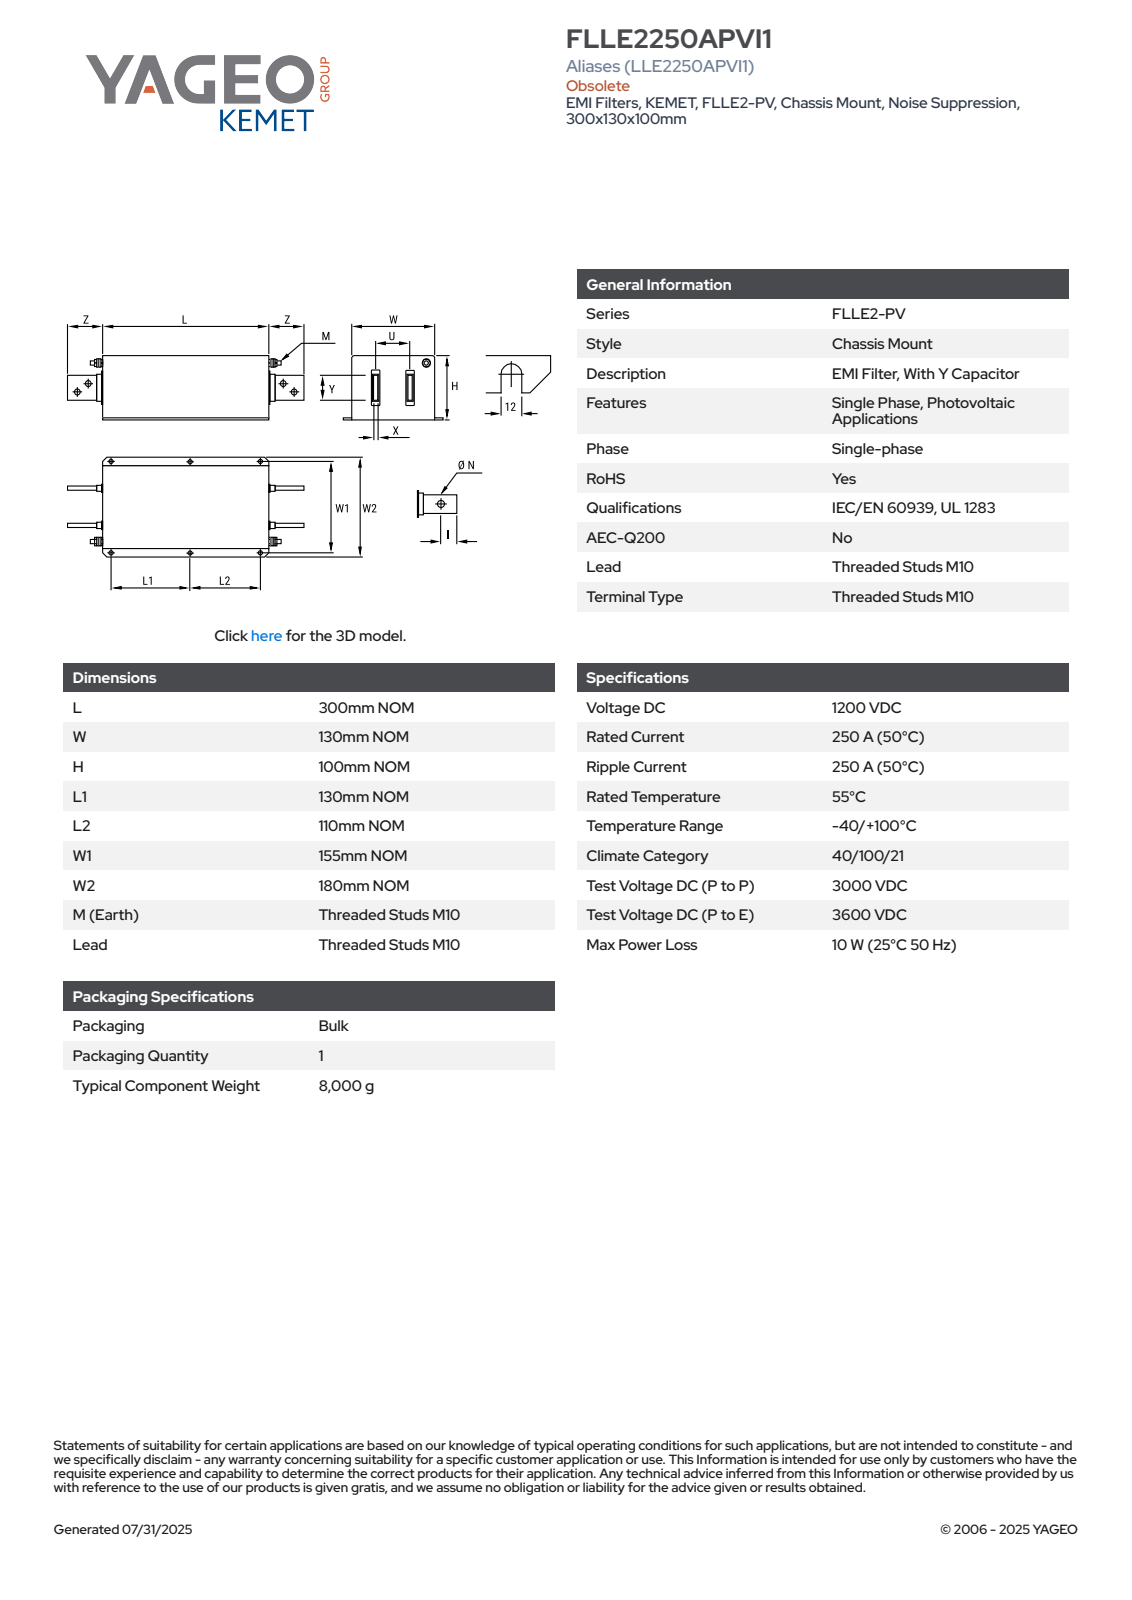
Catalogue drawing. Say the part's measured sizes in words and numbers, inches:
The part is named "HEX NUT M10x1.5_90592A024; HEX BOLT M10x35_91280A636; LOCK WASHER M10_91169A210; Busbar 5x20^FLLE2250APVI1_EXT (+8 more)". Its 3-D file was written by "SolidWorks 2021 (AUTOMOTIVE_DESIGN)". It is 56 solids with 1898 faces: 500 planar, 556 cylindrical and 842 other. Overall it measures 16.378 by 7.087 by 3.937 inches. Its volume is 24.59 cubic inches and its surface area 700.2 square inches. Round holes: 12 of diameter 0.071, 8 of diameter 0.134, 4 of diameter 0.126, 2 of diameter 0.354, 1 of diameter 0.413, 1 of diameter 0.472. Round bosses or shafts: 8 of diameter 0.126, 1 of diameter 0.787, 1 of diameter 0.394. Partial cylindrical surfaces (rounded edges, fillets, slot ends): 40 of radius 0.079, 34 of radius 0.02, 22 of radius 0.01, 22 of radius 0.039, 10 of radius 0.098, 6 of radius 0.236, 4 of radius 0.059, 2 of radius 0.118. The main face-to-face distances are 0.079, 0.039, 5.039, 3.858, 3.937, 3.819, 3.898, 11.732, 4.961, 5.118. The hole center spacings are 1.085, 1.106, 1.418, 1.499, 1.969, 2.313, 2.323, 2.684.
